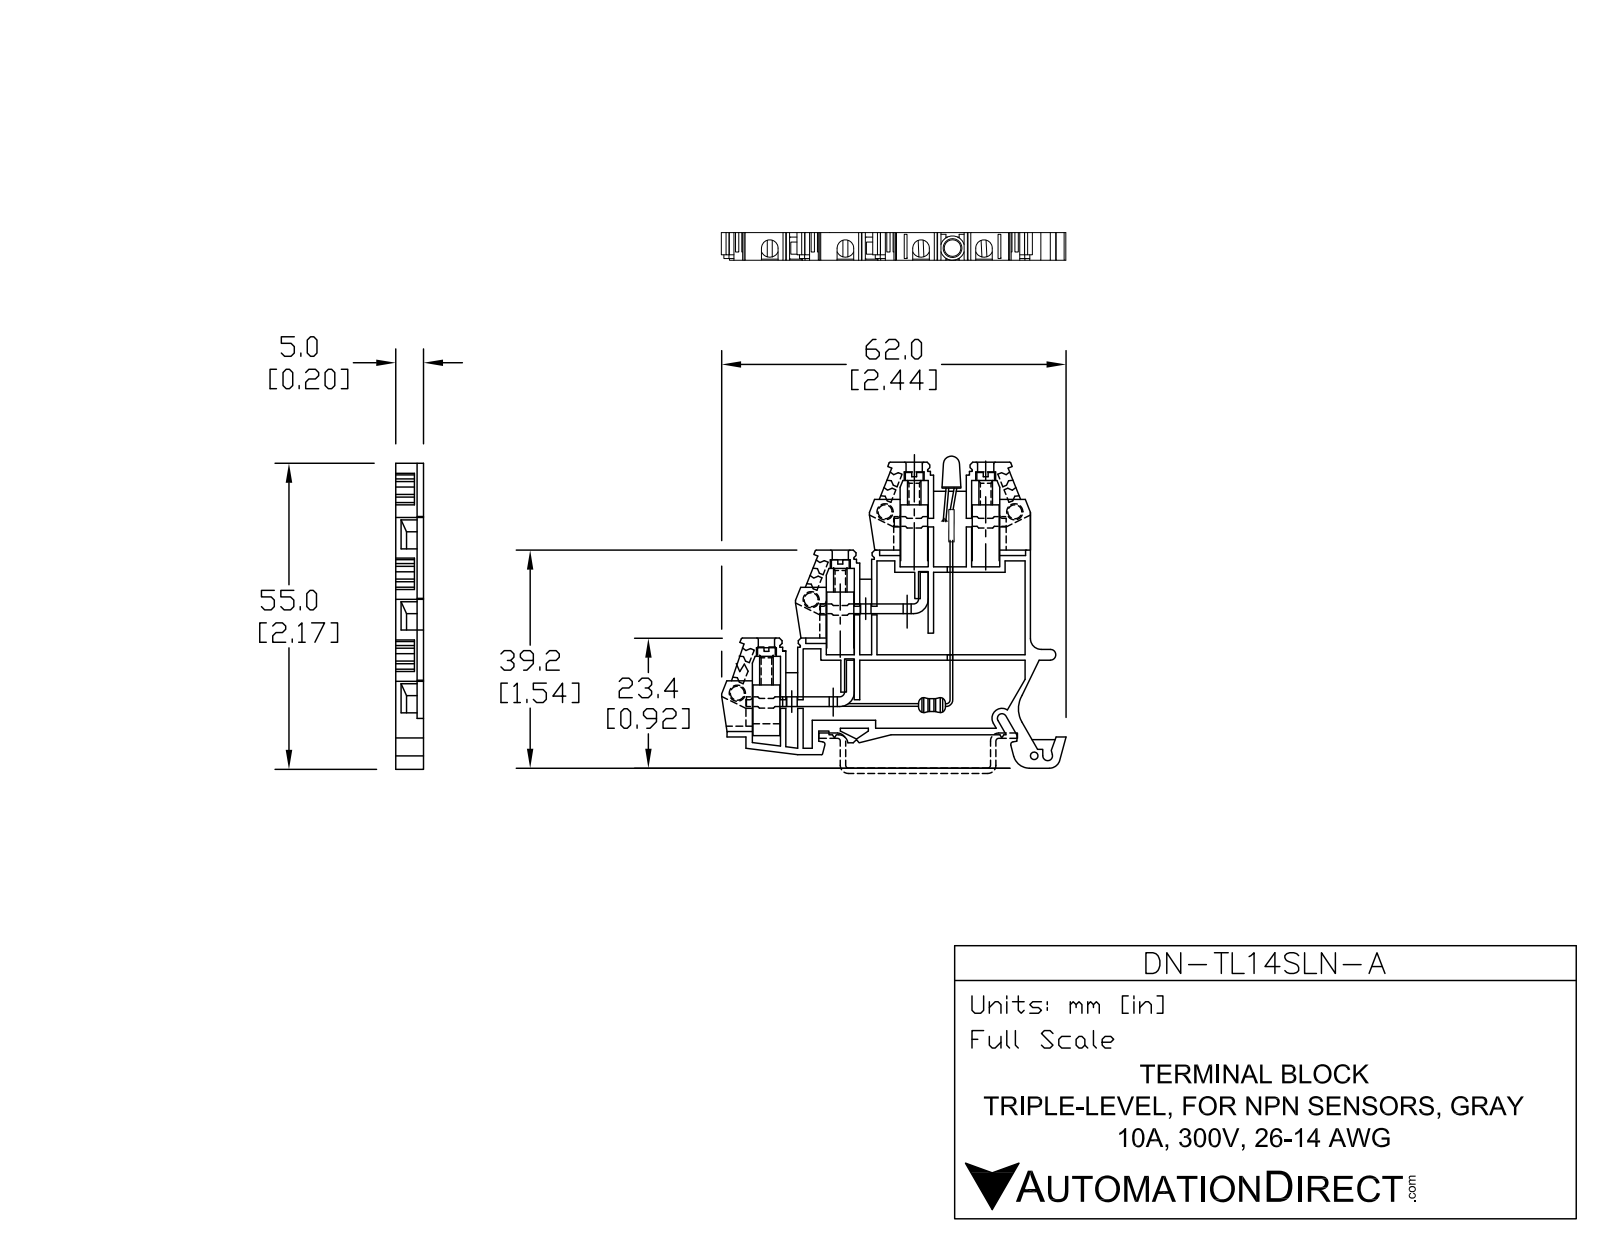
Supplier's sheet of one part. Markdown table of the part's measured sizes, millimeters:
| quantity | value |
| --- | --- |
| part name | 20621; 43505_DN-TL14S-A; 43505LN_DN-TL14SLN-A |
| STEP written by | SolidWorks 2013 (AUTOMOTIVE_DESIGN) |
| units | millimeters |
| bodies | 2 solids, 384 faces (299 planar, 67 cylindrical, 18 other) |
| overall size | 62.39 × 54.1 × 5 |
| volume | 9 099 mm³ |
| surface area | 6 248 mm² |
| round holes (diameter × count) | 2.6 × 4, 1.4 × 1 |
| round bosses / shafts (diameter × count) | 0.3 × 10, 4 × 1, 3 × 1 |
| partial cylindrical surfaces (radius × count) | 0.5 × 8, 0.2 × 4, 1.5 × 4, 1.85 × 4, 2 × 2, 0.3 × 1, 0.85 × 1, 0.9 × 1 |
| main face-to-face distances | 5, 15.3, 1, 4, 2.2, 2, 7.07, 11.9, 13.7, 30.6 |
| hole center spacings | 20.54, 22.2, 39.02, 41.07, 42.35, 47.79, 49.46, 54.45 |
